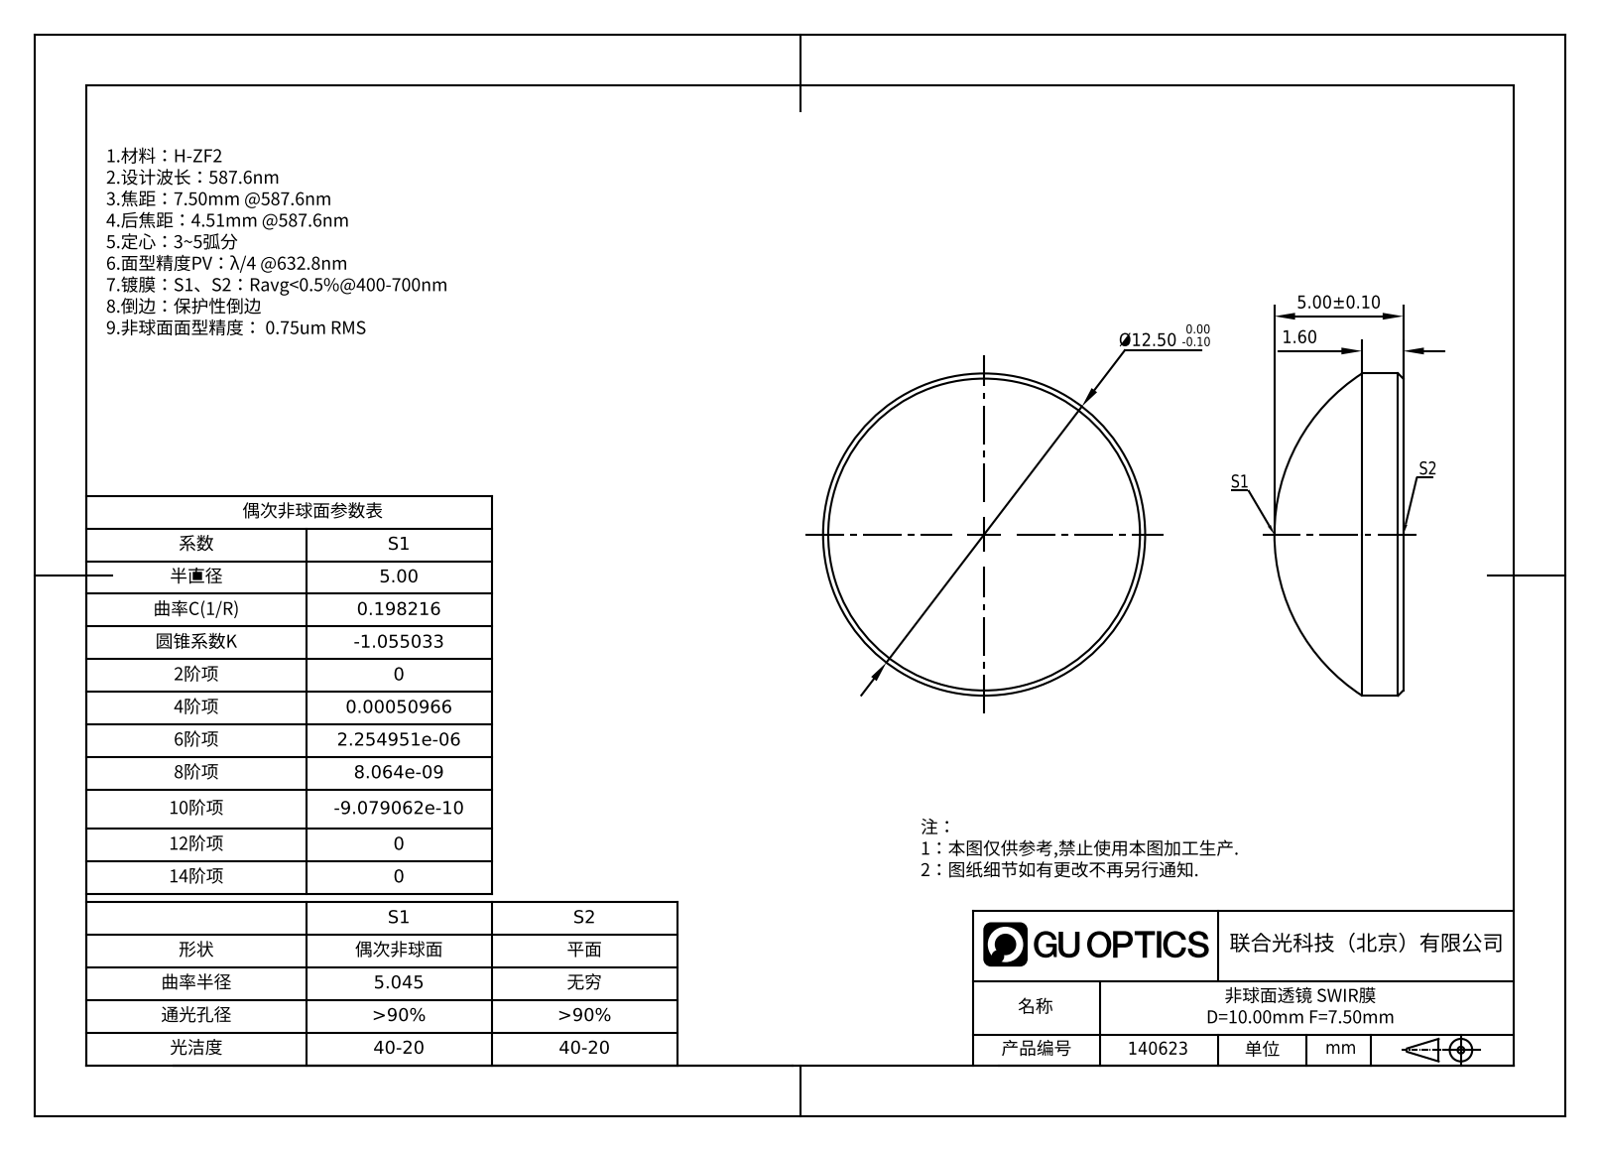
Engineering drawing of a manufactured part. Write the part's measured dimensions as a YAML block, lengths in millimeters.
part_name: "GLA11-012-9.5-SWIR"
step_written_by: "SolidWorks 2022 (AUTOMOTIVE_DESIGN)"
units: millimeters
bodies: {solids: 1, faces: 7, planar: 1, cylindrical: 2, other: 4}
overall_size: [12.5, 12.5, 5]
volume: 425
surface_area: 340
round_bosses_or_shafts:
  - {diameter: 12.5, count: 1}
